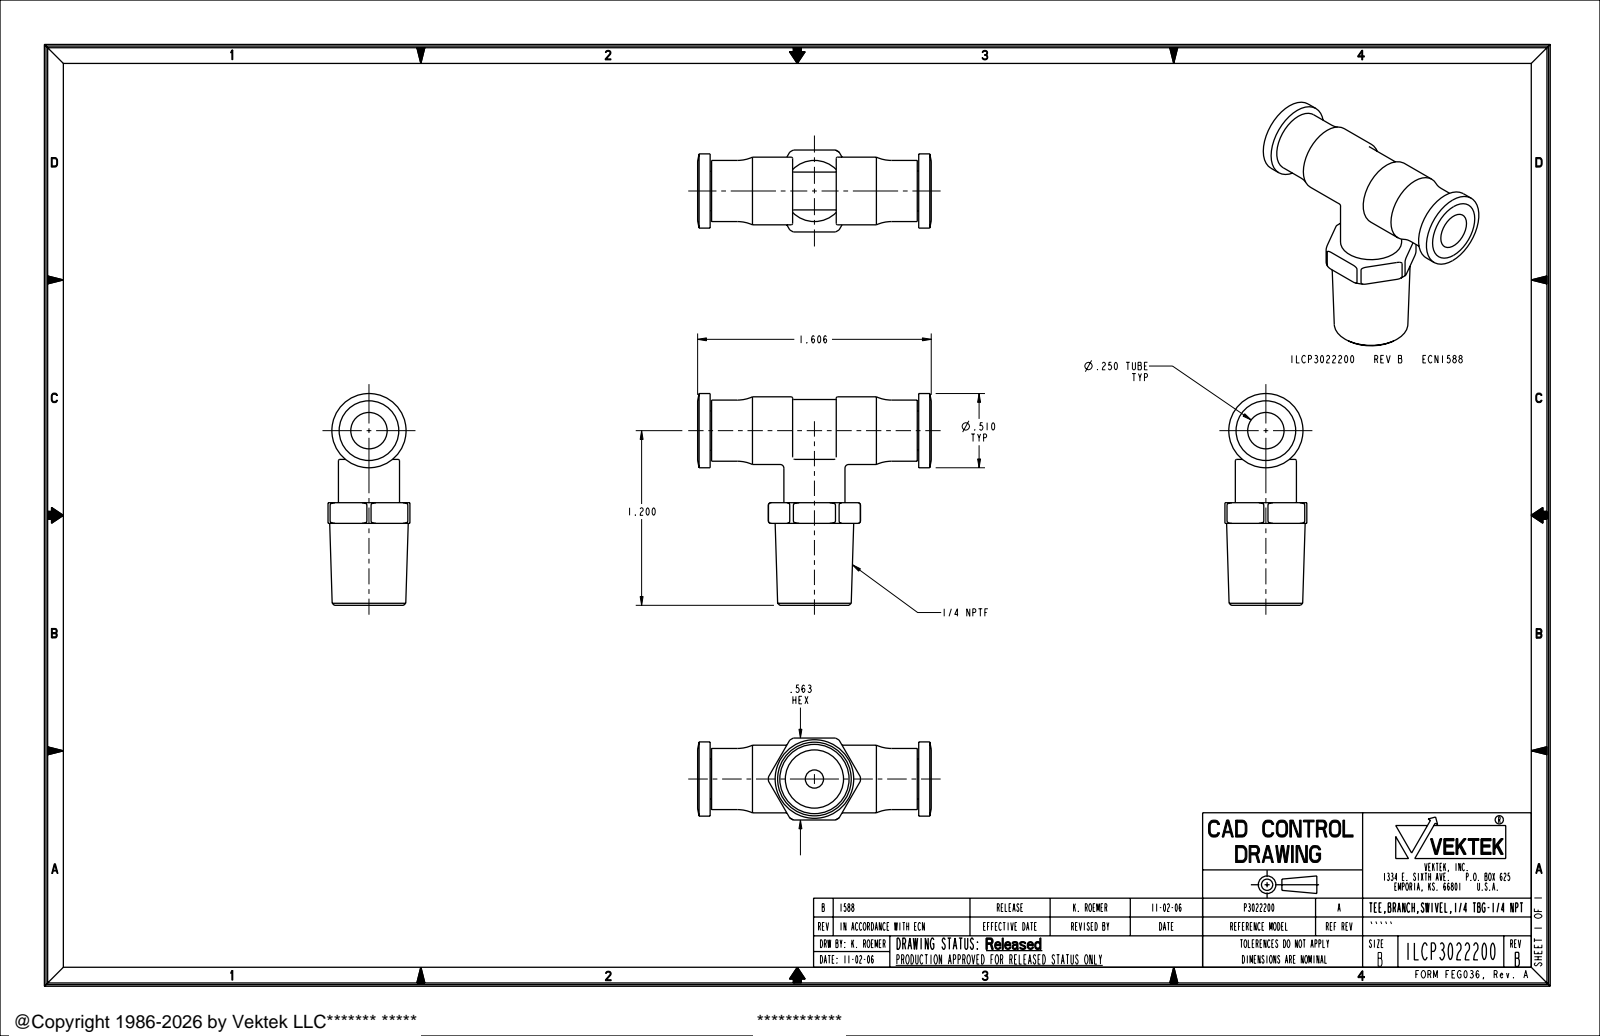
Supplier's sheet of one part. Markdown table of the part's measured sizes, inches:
| quantity | value |
| --- | --- |
| part name | ILCP3022200 |
| STEP written by | PRO/ENGINEER BY PARAMETRIC TECHNOLOGY CORPORATION, 2005180 (AUTOMOTIVE_DESIGN_CC2) |
| units | inches |
| bodies | 1 solid, 131 faces (22 planar, 43 cylindrical, 66 other) |
| overall size | 1.606 × 1.455 × 0.563 |
| volume | 0.274 in³ |
| surface area | 7.171 in² |
| round holes (diameter × count) | 0.125 × 1, 0.25 × 1, 0.4 × 1 |
| round bosses / shafts (diameter × count) | 0.42 × 2, 0.51 × 1, 0.465 × 1, 0.271 × 1 |
| partial cylindrical surfaces (radius × count) | 0.005 × 6, 0.015 × 2, 0.02 × 2, 0.214 × 1, 0.316 × 1 |
| main face-to-face distances | 0.086, 1.52, 0.096, 1.51, 1.424, 1.434, 0.055, 0.26, 0.653, 0.953 |
